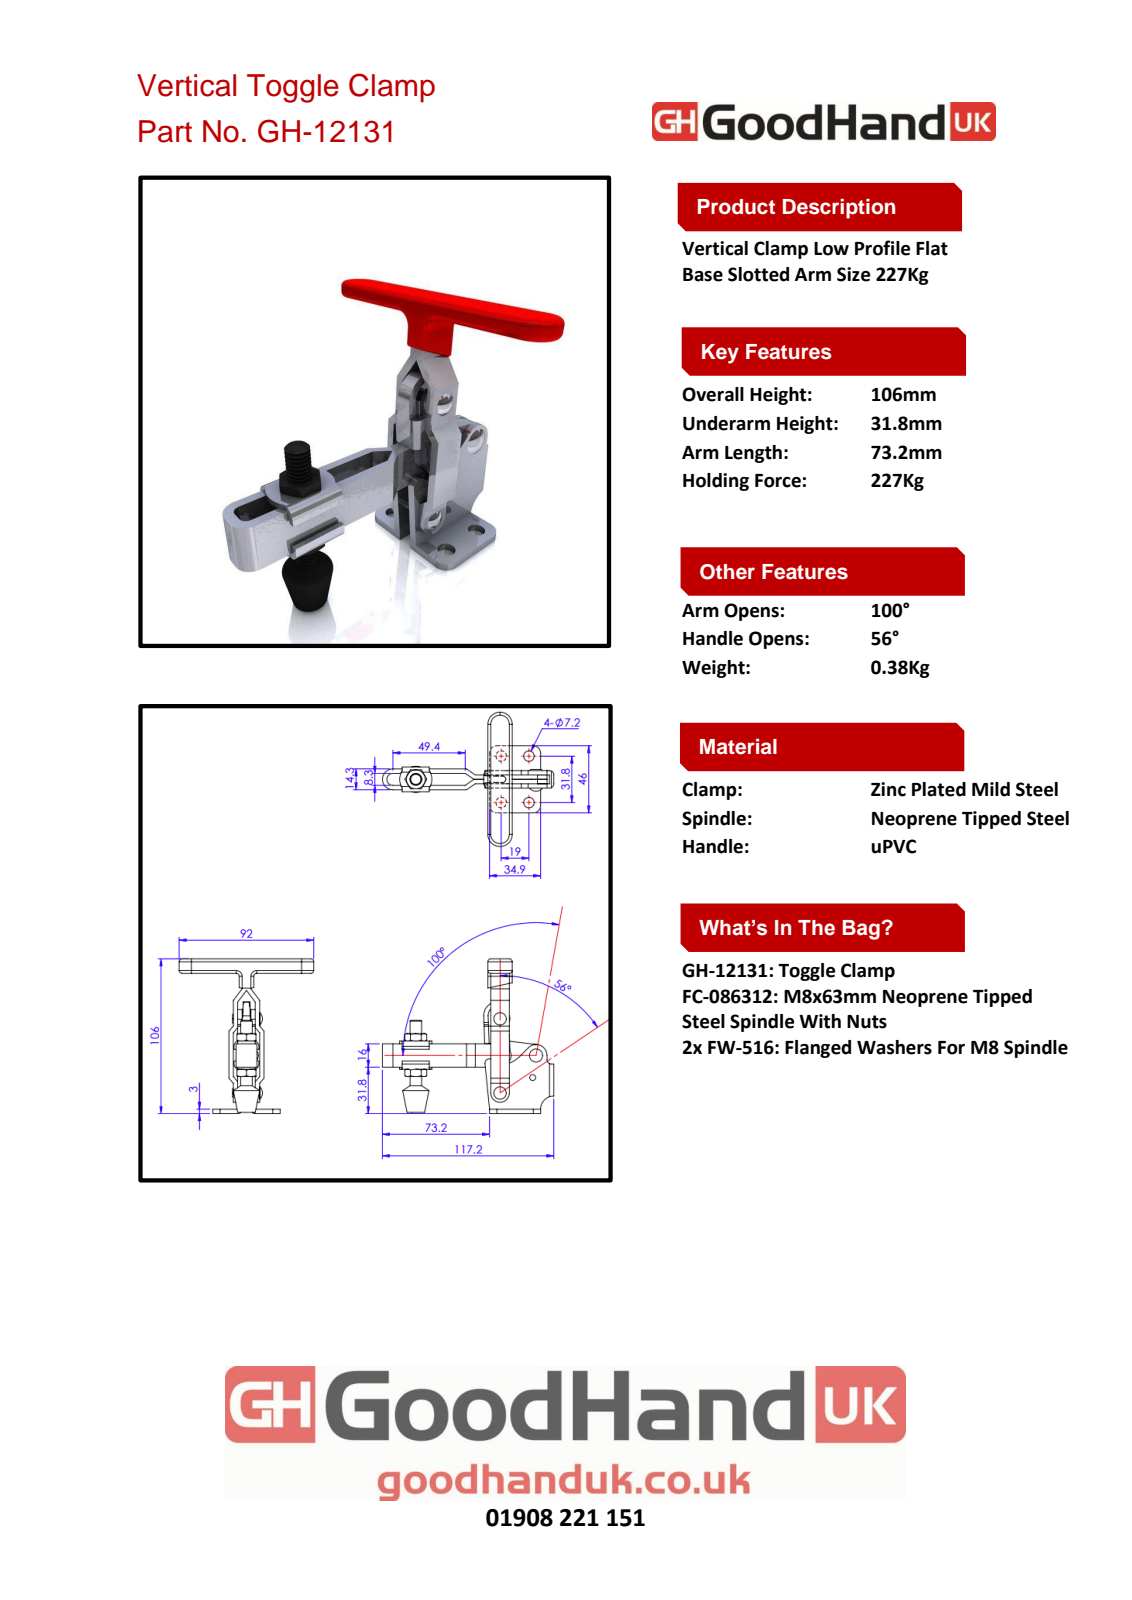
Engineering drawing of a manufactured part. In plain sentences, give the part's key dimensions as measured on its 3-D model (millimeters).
The part is named "Group1^EMC12141; Group4^GH-12131(簡化); Group2^GH-12131(簡化); 11213009-1^GH-12131(簡化) (+2 more)". Its 3-D file was written by "SolidWorks 2016 (AUTOMOTIVE_DESIGN)". It is 5 solids with 307 faces: 155 planar, 99 cylindrical and 53 other. Overall it measures 117.19 by 106 by 92 millimeters. Its volume is 59 367 cubic millimeters and its surface area 37 882 square millimeters. Round holes: 4 of diameter 4, 4 of diameter 7.2. Round bosses or shafts: 2 of diameter 6.4, 2 of diameter 6.3, 1 of diameter 7.93. Partial cylindrical surfaces (rounded edges, fillets, slot ends): 4 of radius 1.5, 4 of radius 3, 4 of radius 5, 4 of radius 7.5, 2 of radius 1, 2 of radius 6.4, 2 of radius 8.35, 2 of radius 9. The main face-to-face distances are 3, 6, 9, 12, 1.15, 4.15, 7.15, 10.15, 13.15, 1.85. The hole center spacings are 19, 31.8, 37.04, 23.4, 25.13, 25.73, 35.14, 35.58.
